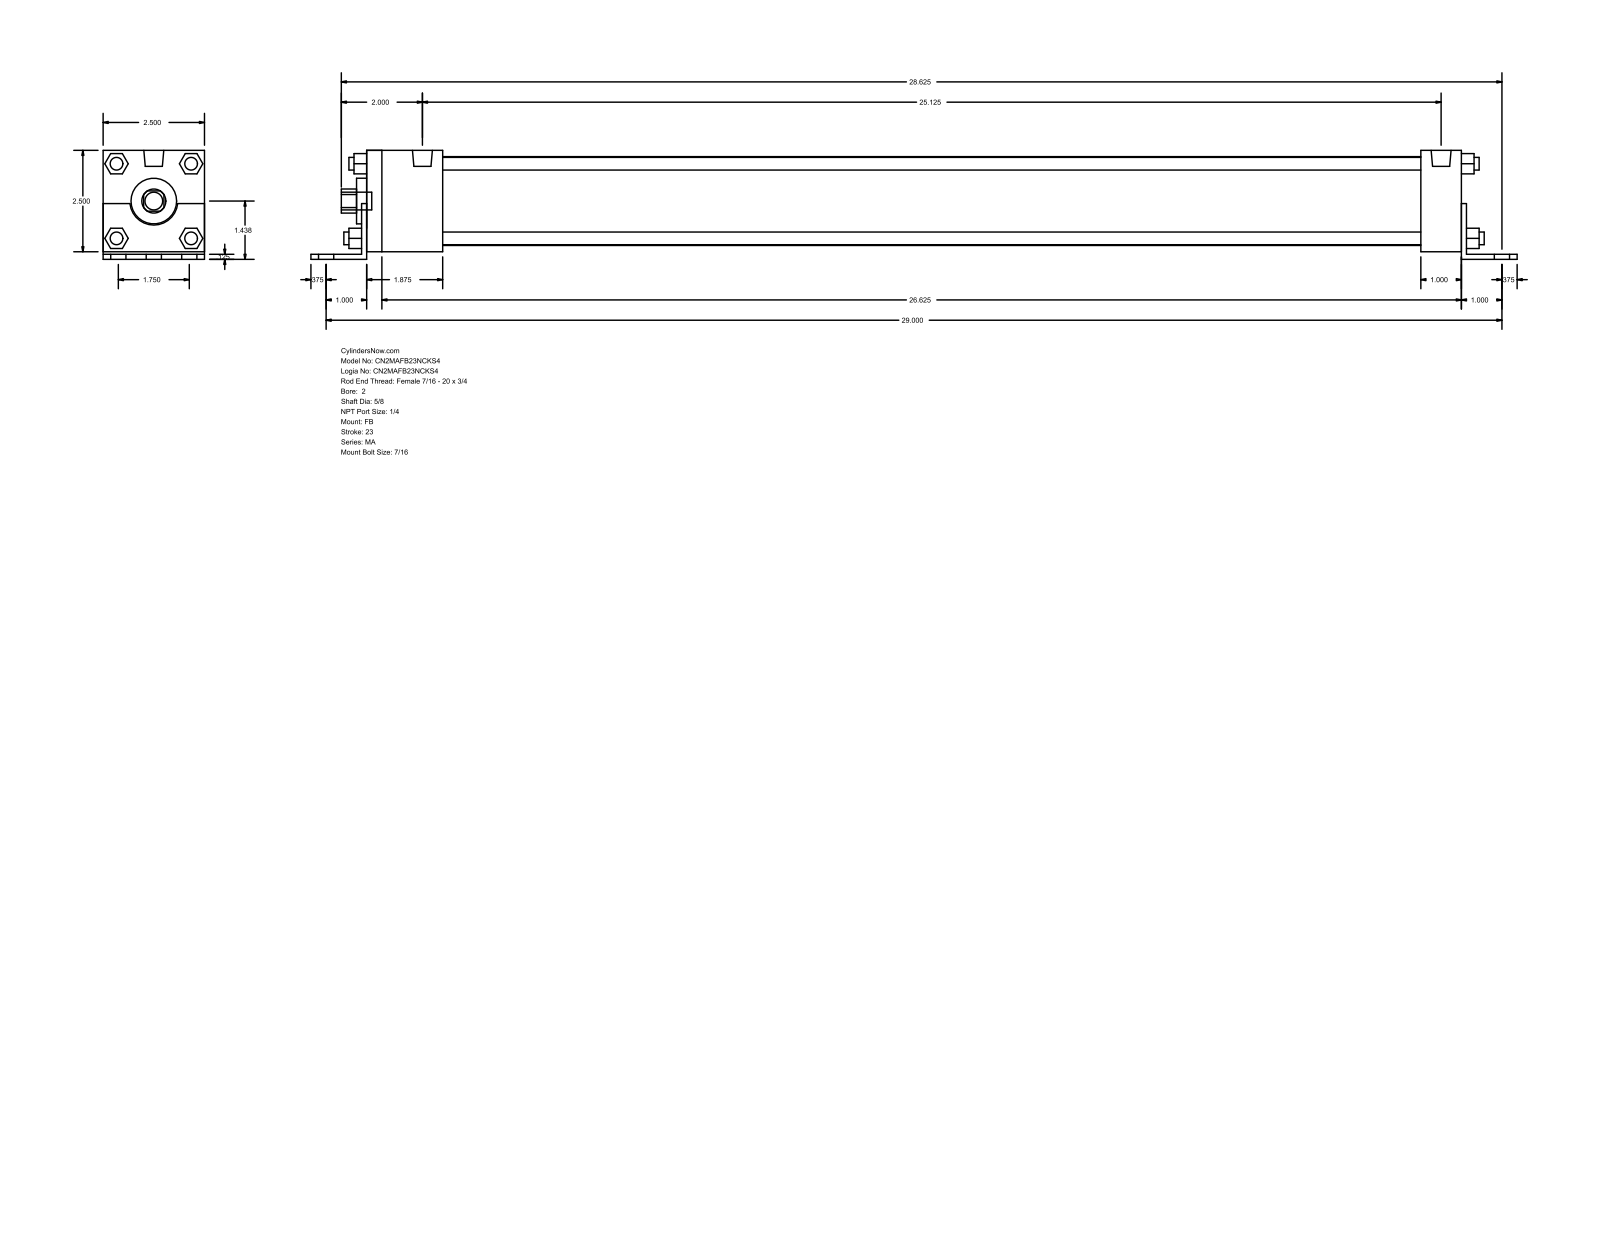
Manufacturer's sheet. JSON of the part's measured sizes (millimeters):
{"part_name": "MA_FB__0200_0.625", "step_written_by": "GSSL Pune (CONFIG_CONTROL_DESIGN)", "units": "millimeters", "bodies": {"solids": 0, "faces": 140, "planar": 105, "cylindrical": 35, "other": 0}, "overall_size": [755.65, 68.26, 63.5], "round_holes": [[15.88, 1], [28.57, 1], [55.63, 1]], "round_bosses_or_shafts": [[7.94, 8], [11.11, 7], [12.49, 2]], "partial_cylinders_radius": [[7.54, 1], [15.05, 1]], "face_to_face_distances": [63.5, 4.76, 3.17, 68.26, 1.59, 3.18, 65.09, 688.97, 685.79, 25.4]}
